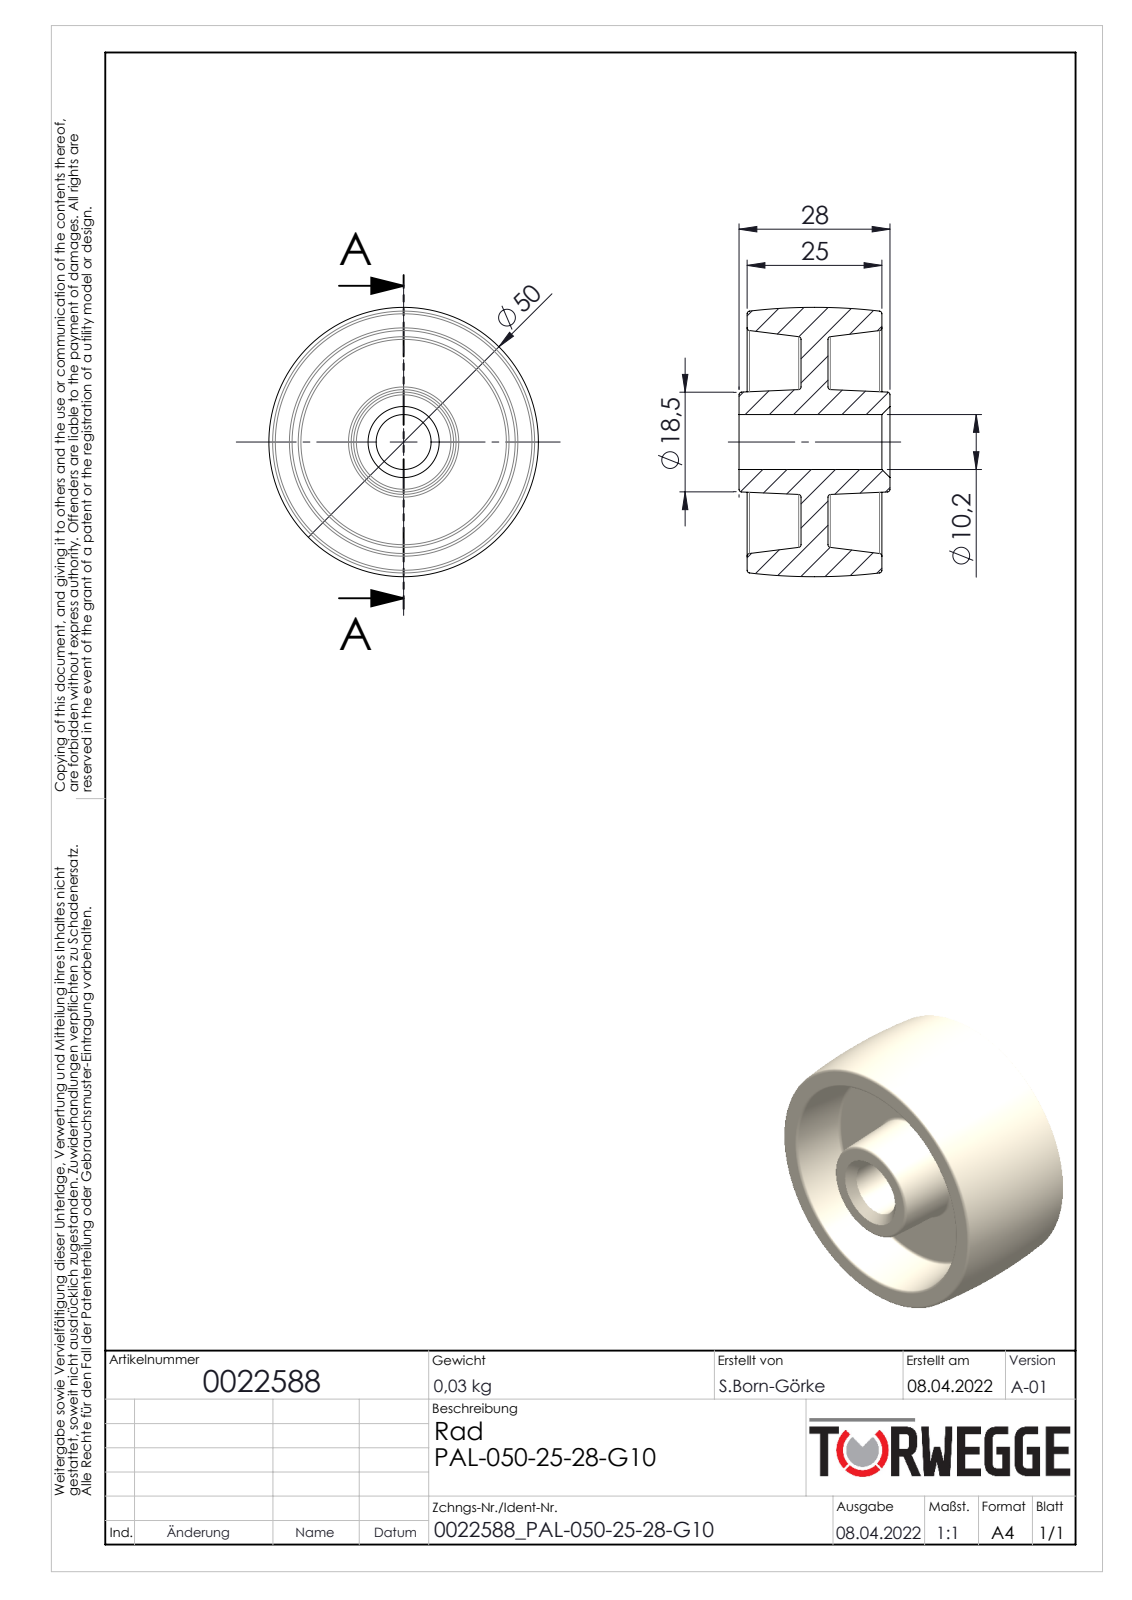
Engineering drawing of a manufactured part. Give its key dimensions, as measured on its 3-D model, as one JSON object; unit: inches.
{"part_name": "0022588", "step_written_by": "SolidWorks 2020 (AUTOMOTIVE_DESIGN)", "units": "inches", "bodies": {"solids": 1, "faces": 42, "planar": 6, "cylindrical": 2, "other": 34}, "overall_size": [1.969, 1.969, 1.102], "volume_in3": 1.639, "surface_area_in2": 18.09, "round_holes": [[0.402, 1]], "face_to_face_distances": [0.197, 0.394, 0.591, 0.984, 0.059, 0.453, 0.65, 1.043, 1.102]}
